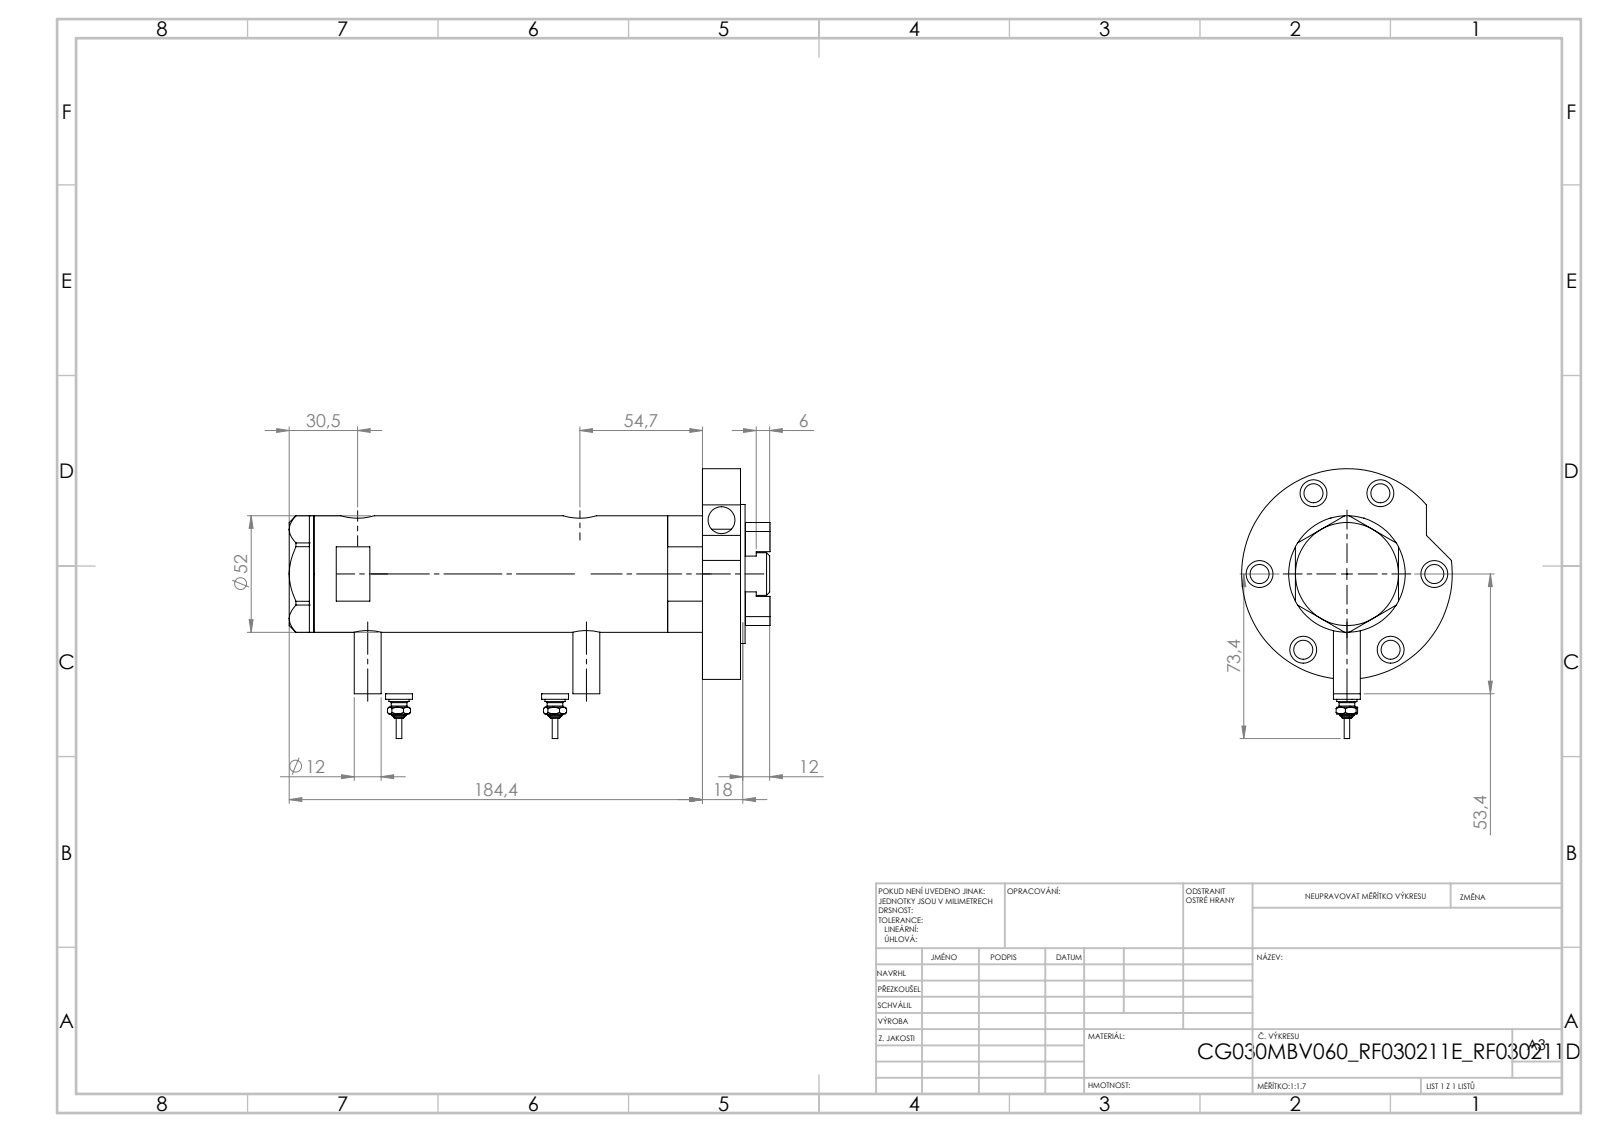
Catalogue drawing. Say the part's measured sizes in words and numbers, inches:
The part is named "V270CG_FRONT; V270CG_RF211E; V270CG_VC; V270CG_RF211D (+3 more)". Its 3-D file was written by "SolidWorks 2019 (CONFIG_CONTROL_DESIGN)". It is 9 solids with 330 faces: 130 planar, 126 cylindrical and 74 other. Overall it measures 8.237 by 4.146 by 3.701 inches. Its volume is 28.09 cubic inches and its surface area 175.9 square inches. Round holes: 7 of diameter 0.472, 6 of diameter 0.335, 4 of diameter 0.201, 4 of diameter 0.354, 2 of diameter 0.197, 2 of diameter 0.383, 2 of diameter 0.492, 2 of diameter 0.591, 1 of diameter 0.256, 1 of diameter 0.787, 1 of diameter 0.846, 1 of diameter 1.181. Round bosses or shafts: 3 of diameter 0.472, 2 of diameter 0.354, 2 of diameter 0.276, 2 of diameter 0.171, 2 of diameter 0.094, 1 of diameter 3.701, 1 of diameter 2.441, 1 of diameter 2.047. The main face-to-face distances are 0.669, 0.079, 2.043, 2.713, 2.791, 0.748, 0.937, 4.904, 6.947, 7.616. The hole center spacings are 1.535, 0.659, 1.479, 1.843, 0.114, 0.177, 0.394, 0.881.
